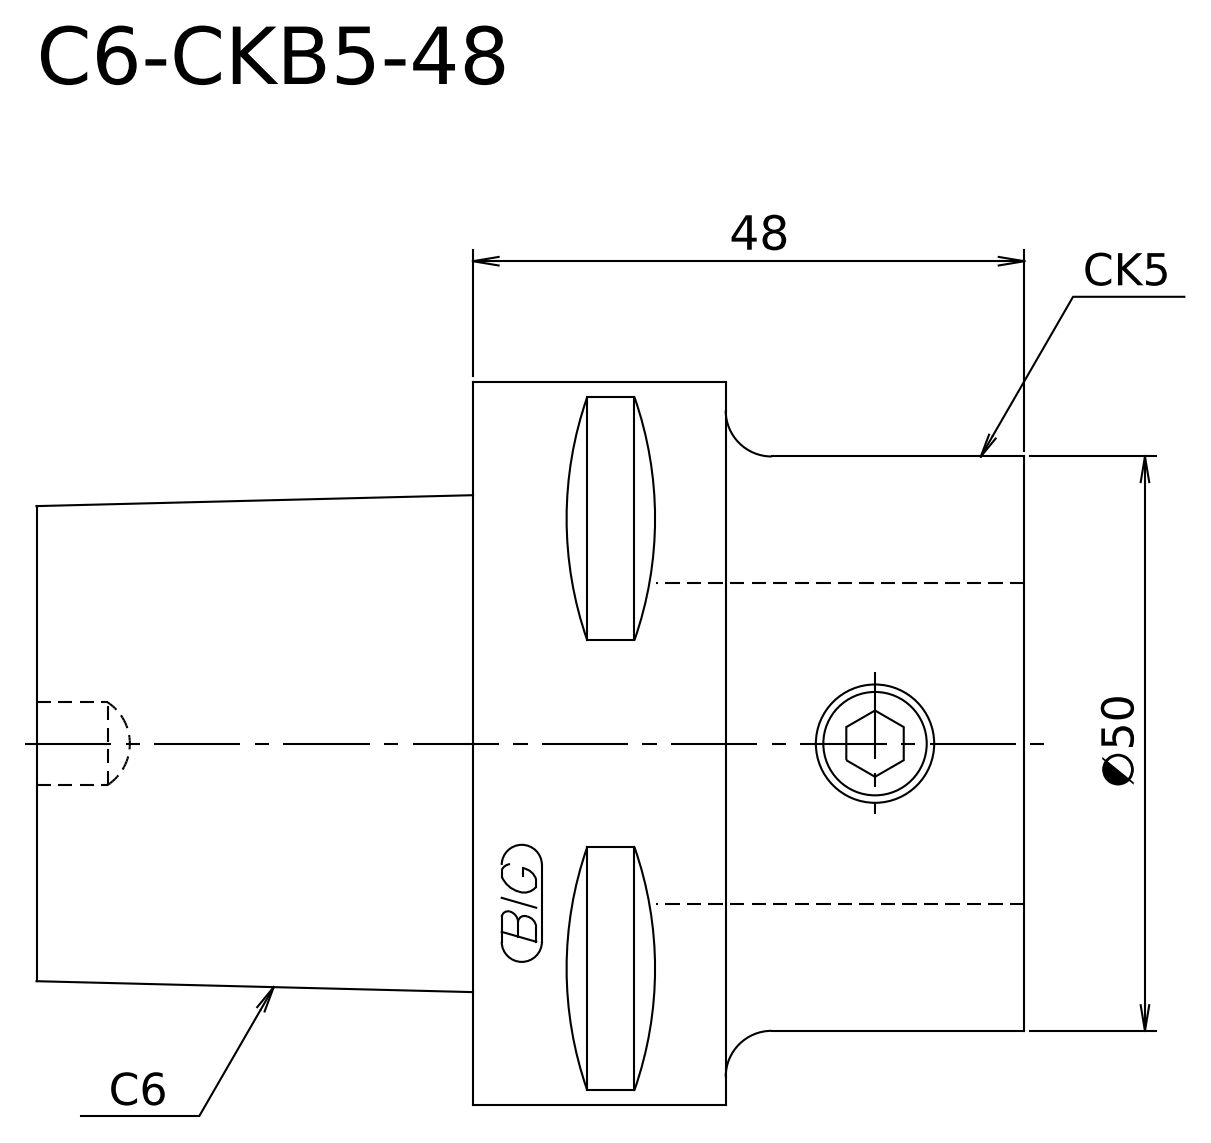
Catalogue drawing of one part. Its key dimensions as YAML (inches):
step_written_by: "Kubotek KeyCreator V8.5.1 (14335) (CONFIG_CONTROL_DESIGN)"
units: inches
bodies: {solids: 1, faces: 10, planar: 4, cylindrical: 2, other: 4}
overall_size: [3.386, 2.48, 2.48]
volume: 10.72
surface_area: 29.99
round_bosses_or_shafts:
  - {diameter: 2.48, count: 1}
  - {diameter: 1.969, count: 1}
face_to_face_distances: [1.89, 3.386, 1.496, 1.024, 0.866, 2.362]
